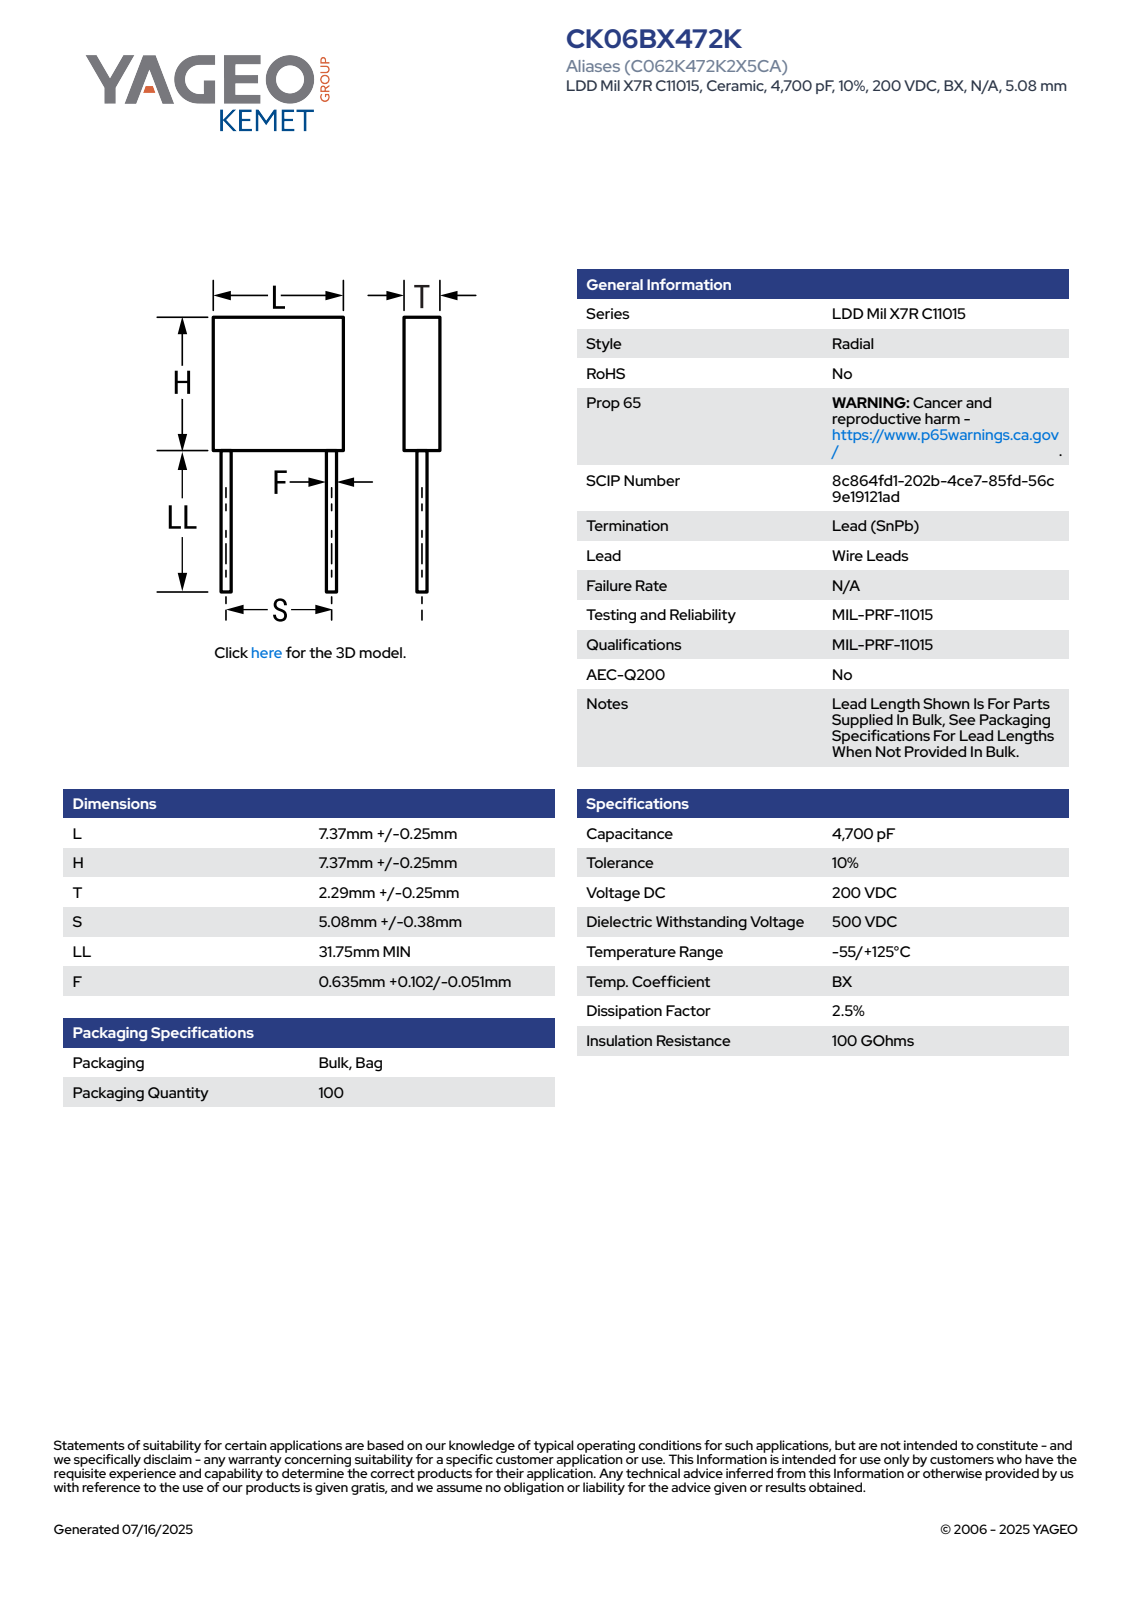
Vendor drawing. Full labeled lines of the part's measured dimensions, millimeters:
Part name (STEP PRODUCT): CCRM_ST_C062_L7.62H7.62T2.54S5.08LL31.75F0.686
STEP written by: SolidWorks 2014 (AUTOMOTIVE_DESIGN)
Units: millimetres
Bodies: 4 solids, 69 faces (65 planar, 4 cylindrical, 0 other)
Overall size (bounding box): 39.37 × 7.62 × 2.54
Volume: 171 mm³ · Surface area: 340 mm²
Round bosses / shafts (diameter × count): ⌀0.69 ×2
Main face-to-face distances: 2.54, 7.62, 31.75, 39.37, 3.19, 4.43, 36.18, 34.94, 1.24, 0.34
